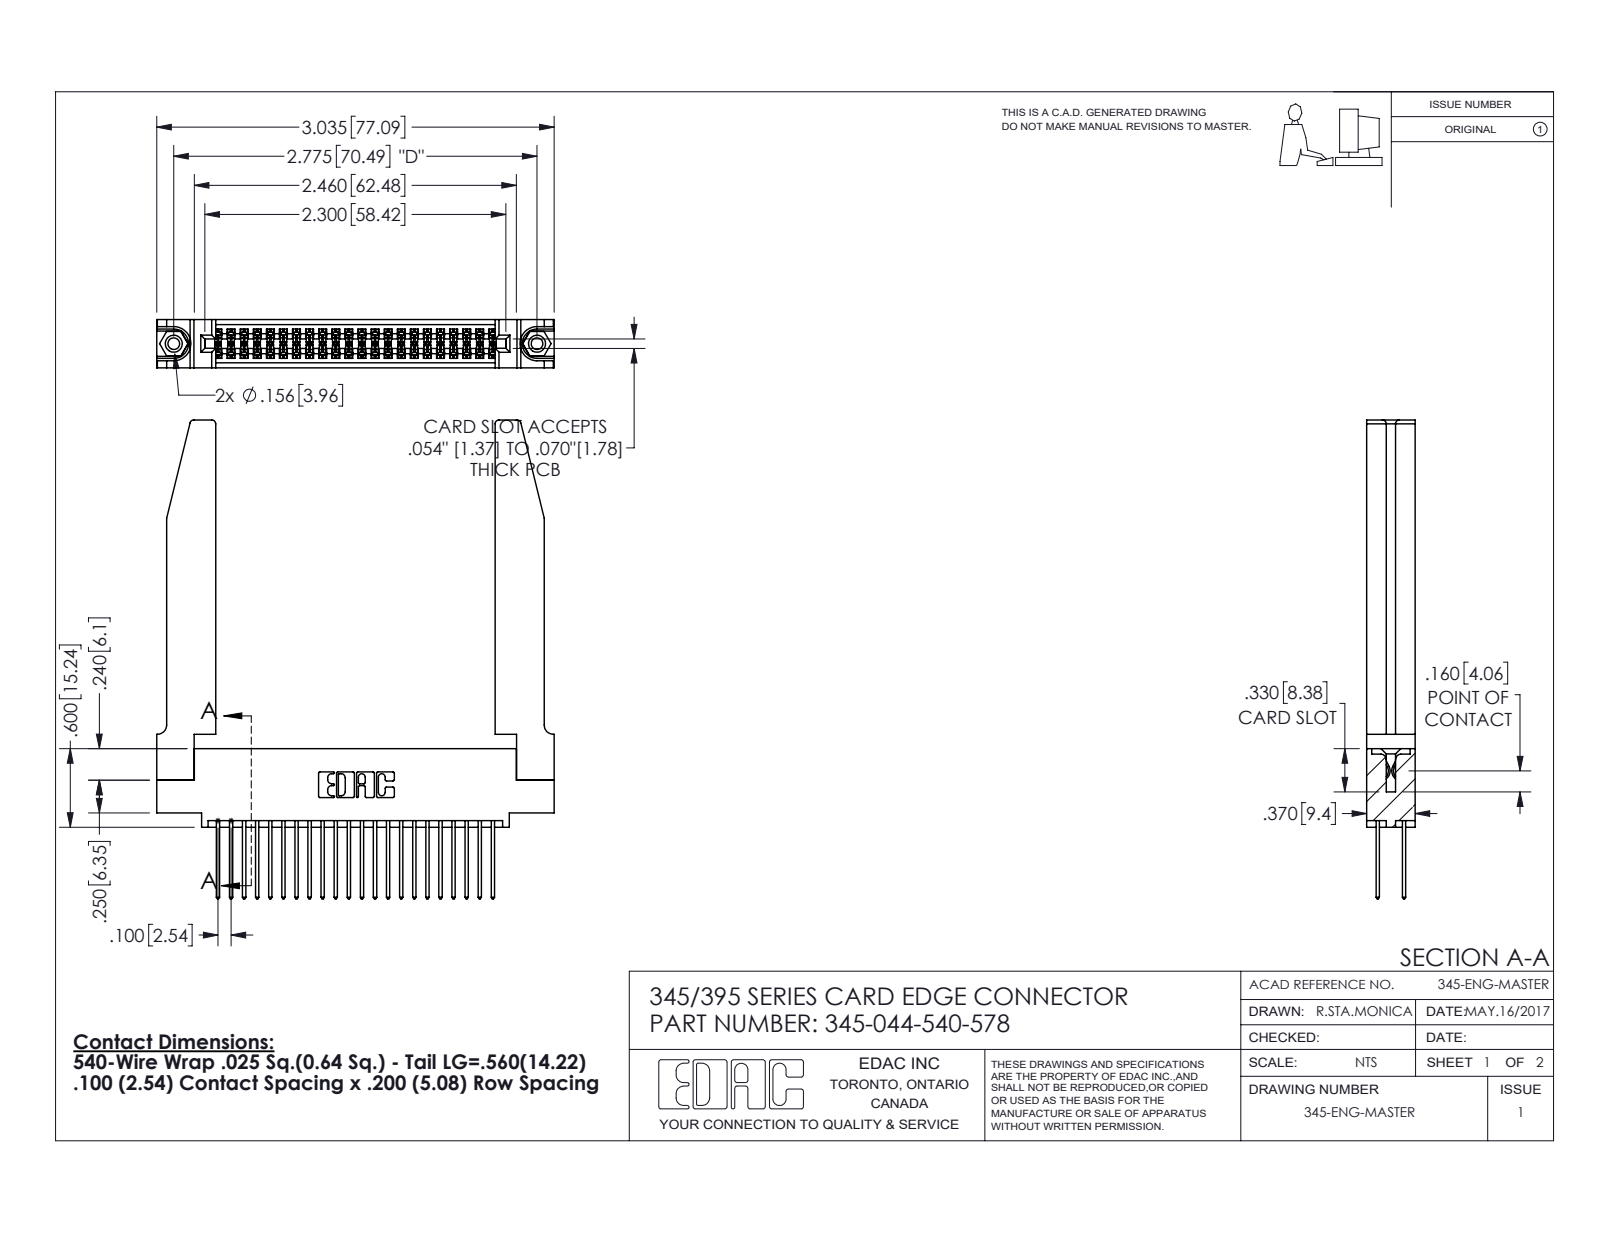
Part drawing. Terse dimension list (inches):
name: 345-292-001_345-293-140; 345-044-540-578; 345-220-078_345-220-078; 345-250-001_345-250-001-102 (+1 more)
written by: SolidWorks 2016 (CONFIG_CONTROL_DESIGN)
unit: in
bodies: 49 solids, 2564 faces (1678 planar, 834 cylindrical, 52 other)
size: 3.657 × 3.036 × 0.37
volume: 0.926 in³; area: 28.29 in²
holes: 2× ⌀0.089, 2× ⌀0.125, 2× ⌀0.156, 1× ⌀0.064
bosses: 2× ⌀0.155
rounds: 66× R0.006, 44× R0.01, 22× R0.01, 8× R0.03, 6× R0.007, 6× R0.031, 3× R0.026, 2× R0.014
face distances: 0.37, 0.072, 0.298, 0.2, 0.098, 0.272, 0.025, 0.225, 0.148, 0.15
hole spacings: 0.27, 2.541, 2.775
